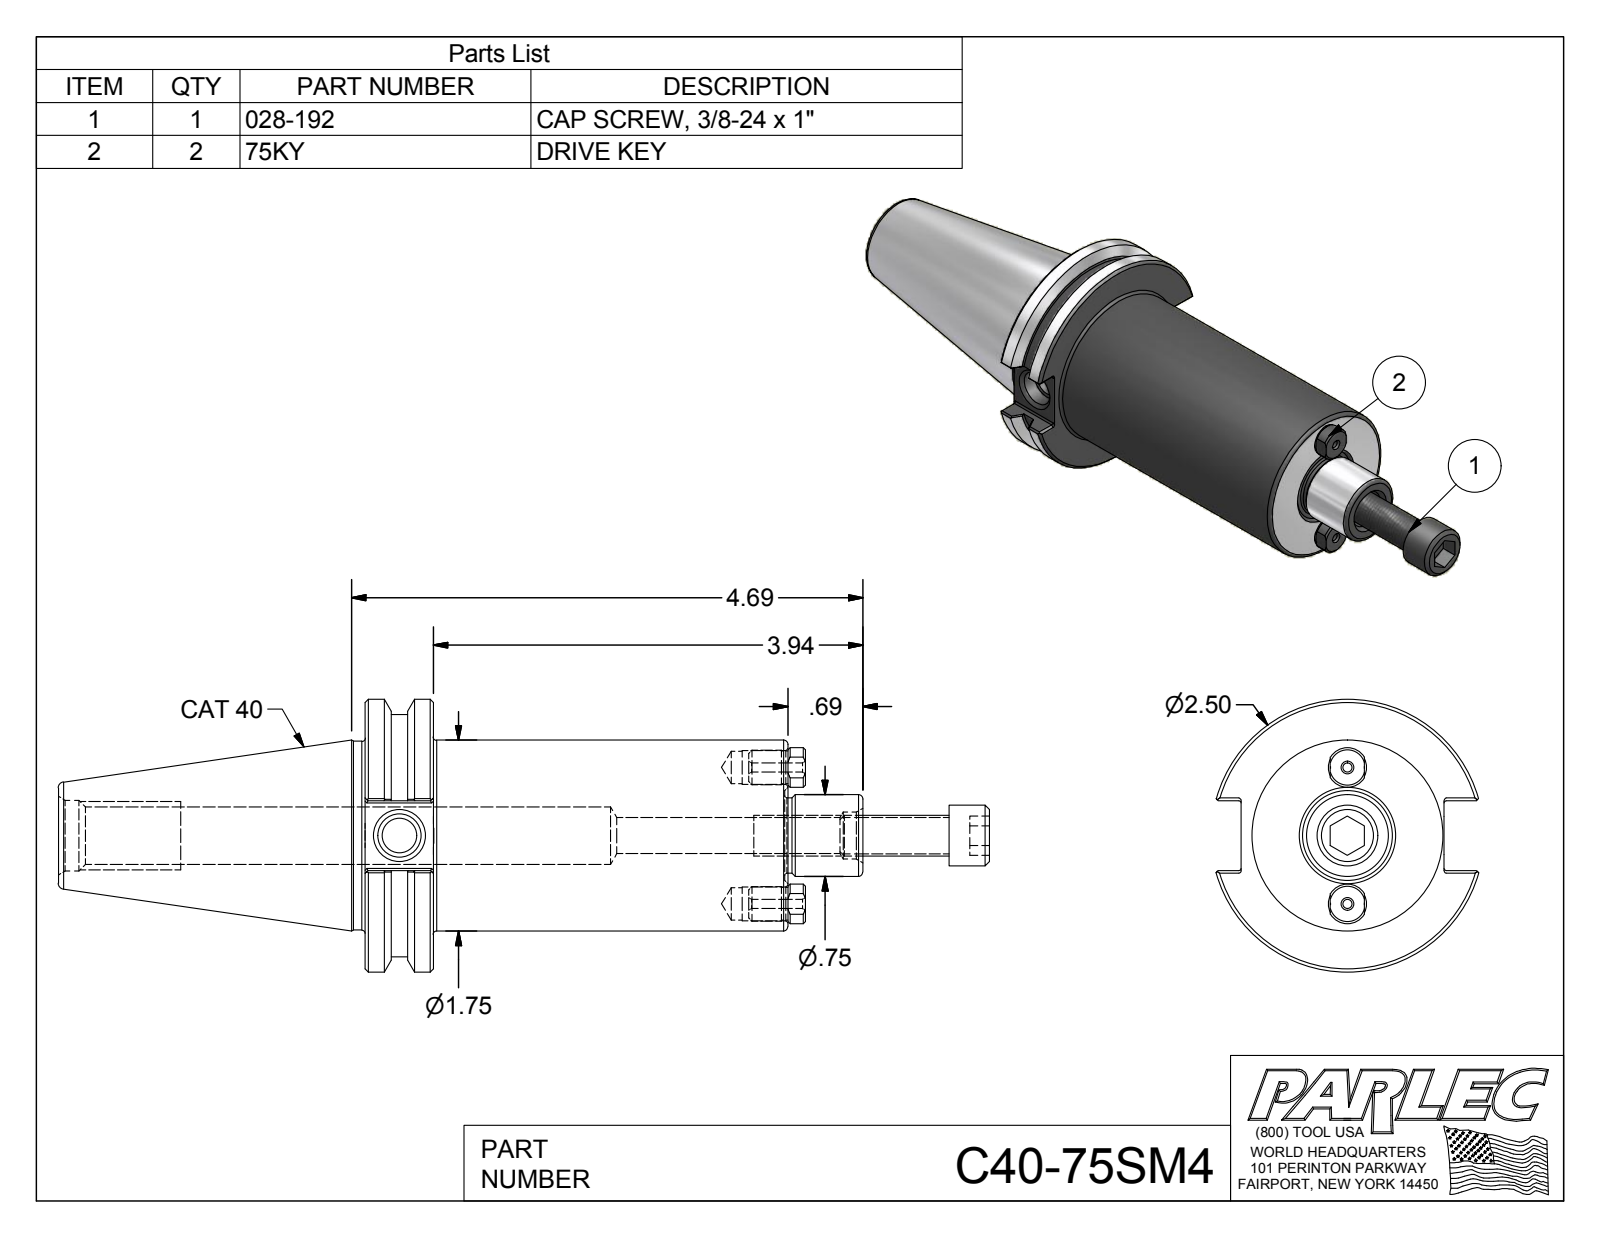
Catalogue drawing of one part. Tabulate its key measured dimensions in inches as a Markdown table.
| quantity | value |
| --- | --- |
| part name | C40-75SM4; C40-75SM4-1; 75KY; 028-192 |
| STEP written by | Autodesk Inventor 2012 (AUTOMOTIVE_DESIGN) |
| units | inches |
| bodies | 4 solids, 154 faces (57 planar, 44 cylindrical, 53 other) |
| overall size | 8.536 × 2.5 × 2.406 |
| volume | 13.84 in³ |
| surface area | 61.16 in² |
| round holes (diameter × count) | 0.084 × 2, 0.297 × 2, 0.312 × 2, 0.315 × 1, 0.33 × 1, 0.399 × 1, 0.43 × 1, 0.527 × 1, 0.648 × 1 |
| round bosses / shafts (diameter × count) | 0.318 × 2, 0.3 × 2, 2.5 × 1, 2.219 × 1, 1.75 × 1, 1.73 × 1, 0.75 × 1, 0.69 × 1 |
| partial cylindrical surfaces (radius × count) | 0.02 × 12, 0.183 × 2 |
| main face-to-face distances | 0.625, 3.875, 3.25, 0.64, 1.86, 2.812, 3.437, 6.687, 3.201, 0.389 |
| hole center spacings | 0.625, 0.625, 1.25, 1.25 |
